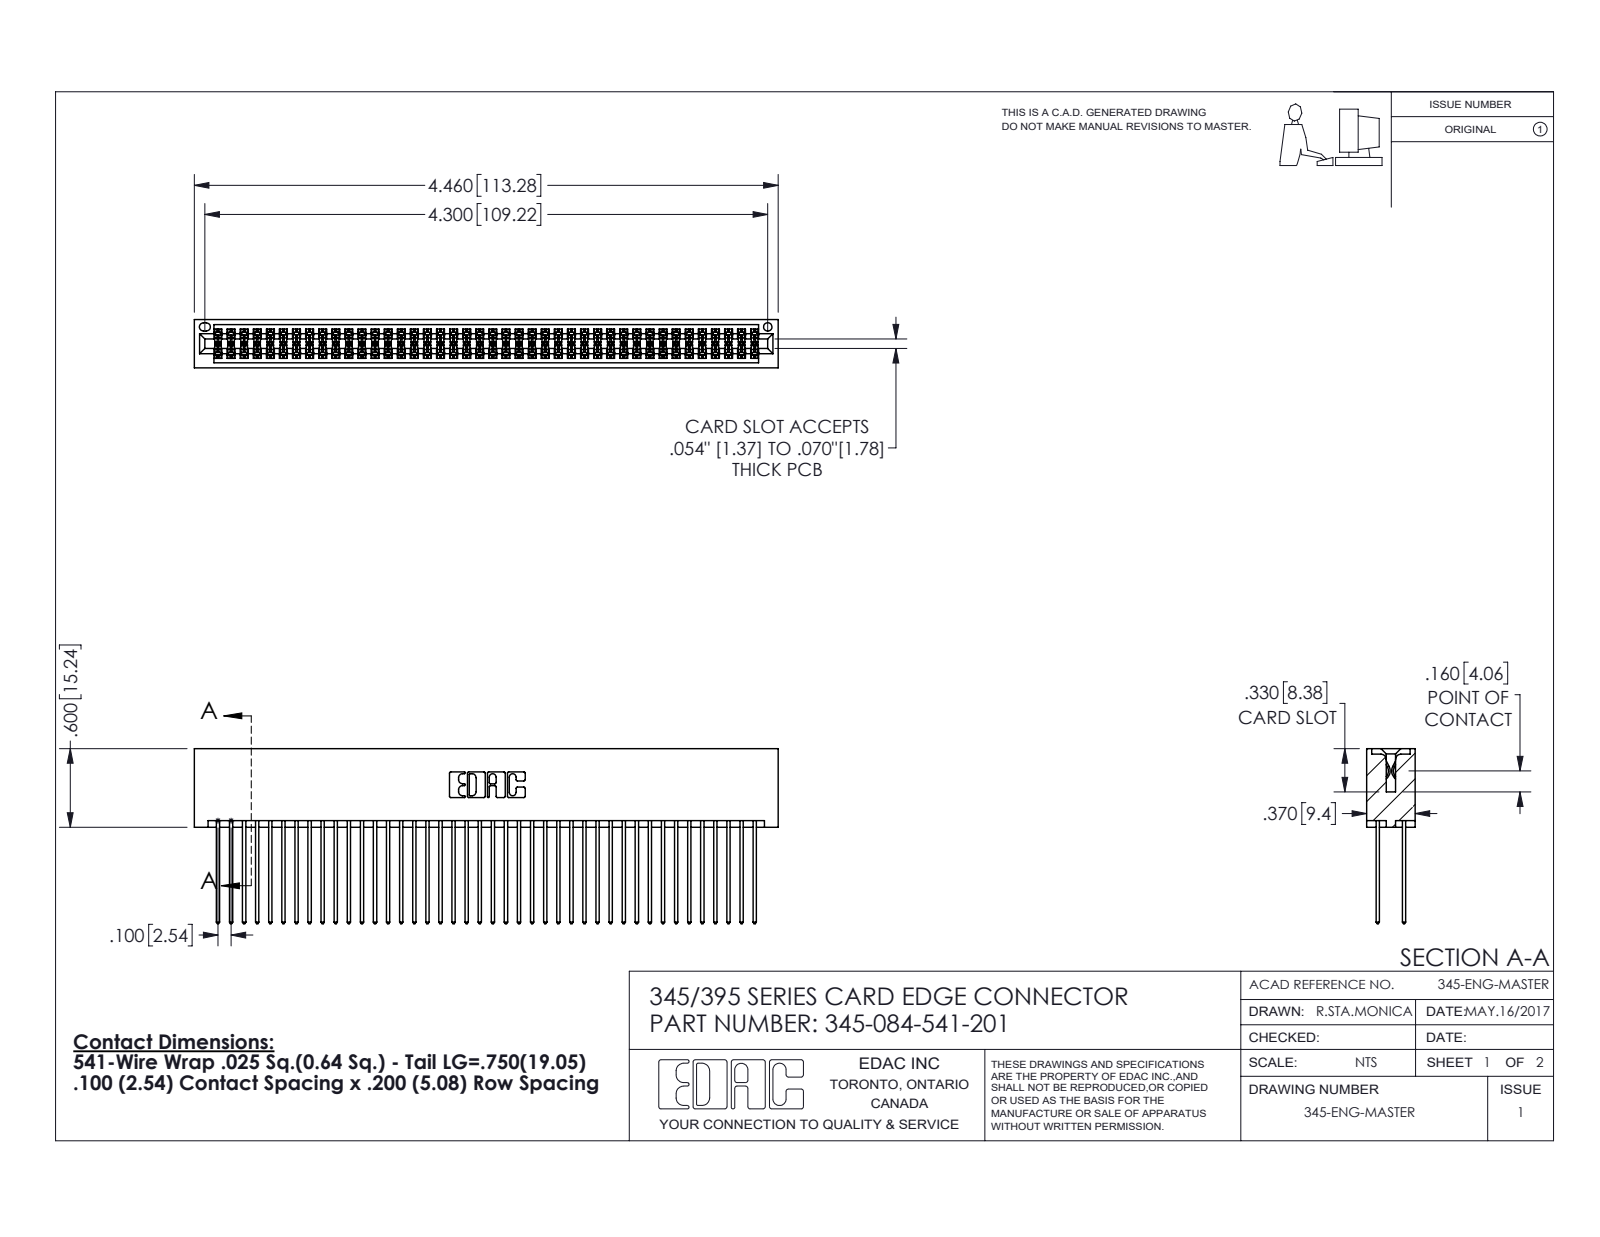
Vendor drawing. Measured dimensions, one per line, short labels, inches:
name: 345-084-541-201; 345-292-001_345-293-141; 345 Part_No Mounting Lugs
written by: SolidWorks 2016 (CONFIG_CONTROL_DESIGN)
unit: in
bodies: 85 solids, 4318 faces (2848 planar, 1470 cylindrical, 0 other)
size: 4.46 × 1.337 × 0.37
volume: 0.739 in³; area: 31.71 in²
holes: 1× ⌀0.064
rounds: 126× R0.006, 84× R0.01, 22× R0.01, 6× R0.007, 6× R0.031, 3× R0.026, 2× R0.014, 2× R0.019
face distances: 0.298, 0.072, 0.2, 0.098, 0.272, 0.025, 0.225, 0.37, 0.175, 0.149
